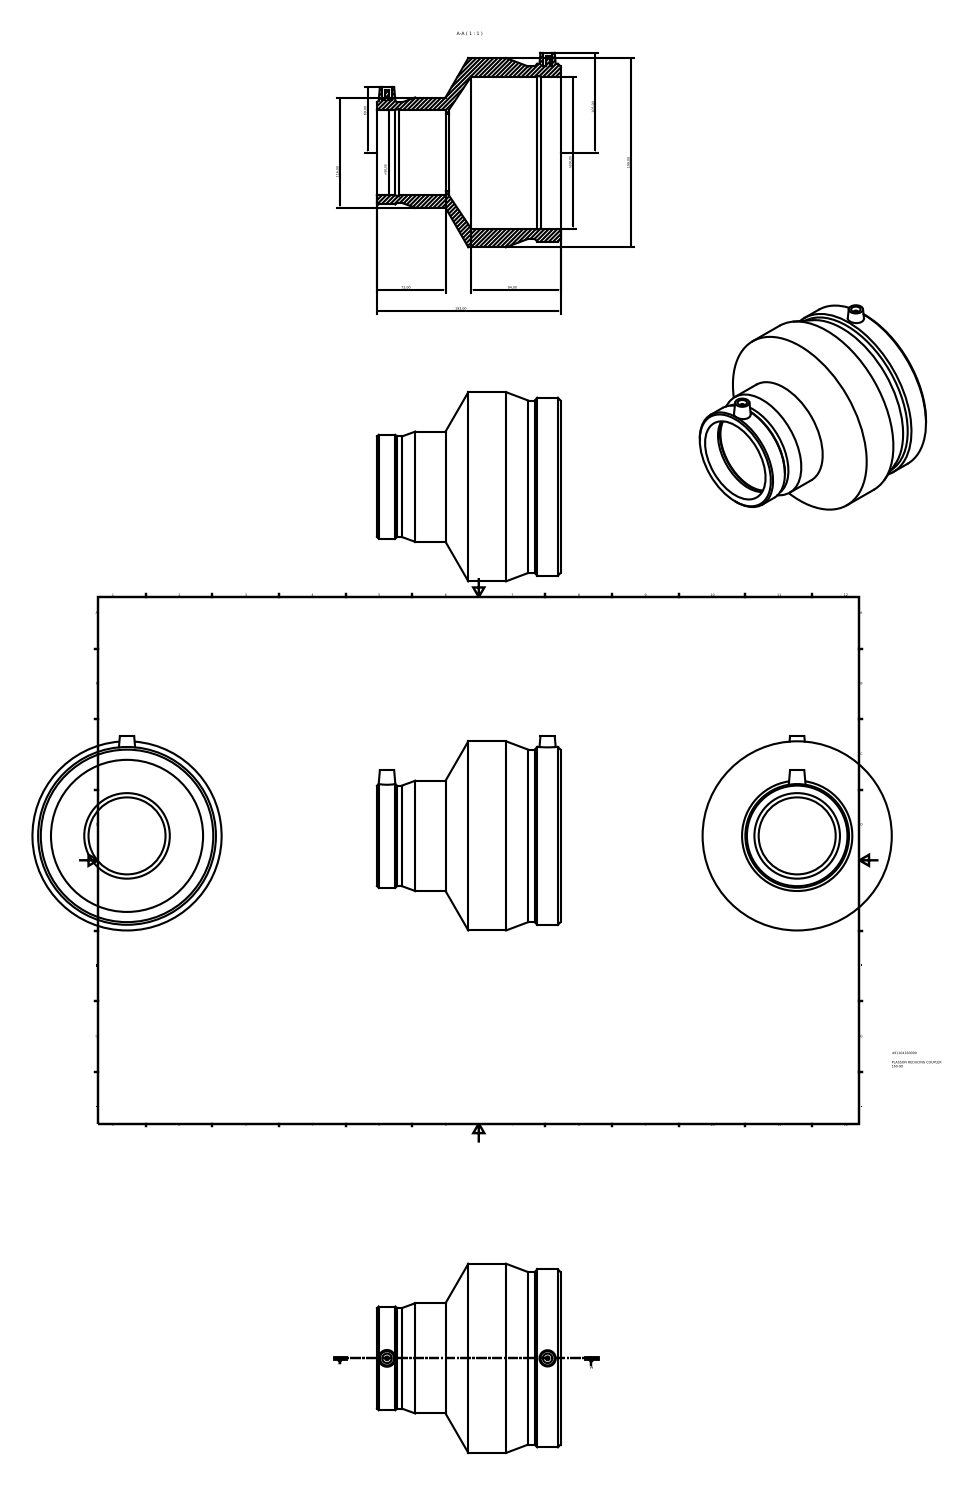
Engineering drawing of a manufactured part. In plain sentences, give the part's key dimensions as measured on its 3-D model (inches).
The part is named "491104160090". Its 3-D file was written by "Autodesk Inventor 2015 (AUTOMOTIVE_DESIGN)". It is 1 solid with 39 faces: 12 planar, 15 cylindrical and 12 other. Overall it measures 8.051 by 7.835 by 7.598 inches. Its volume is 82.26 cubic inches and its surface area 324.7 square inches. Round holes: 2 of diameter 0.394, 1 of diameter 3.189, 1 of diameter 3.543, 1 of diameter 6.299. Round bosses or shafts: 2 of diameter 0.157, 1 of diameter 7.835, 1 of diameter 7.365, 1 of diameter 7.144, 1 of diameter 4.567, 1 of diameter 4.293, 1 of diameter 4.164. The main face-to-face distances are 7.598, 2.976, 4.622, 2.835, 0.142, 4.764, 6.636, 3.801, 3.659, 0.963. The hole center spacings are 6.651.
